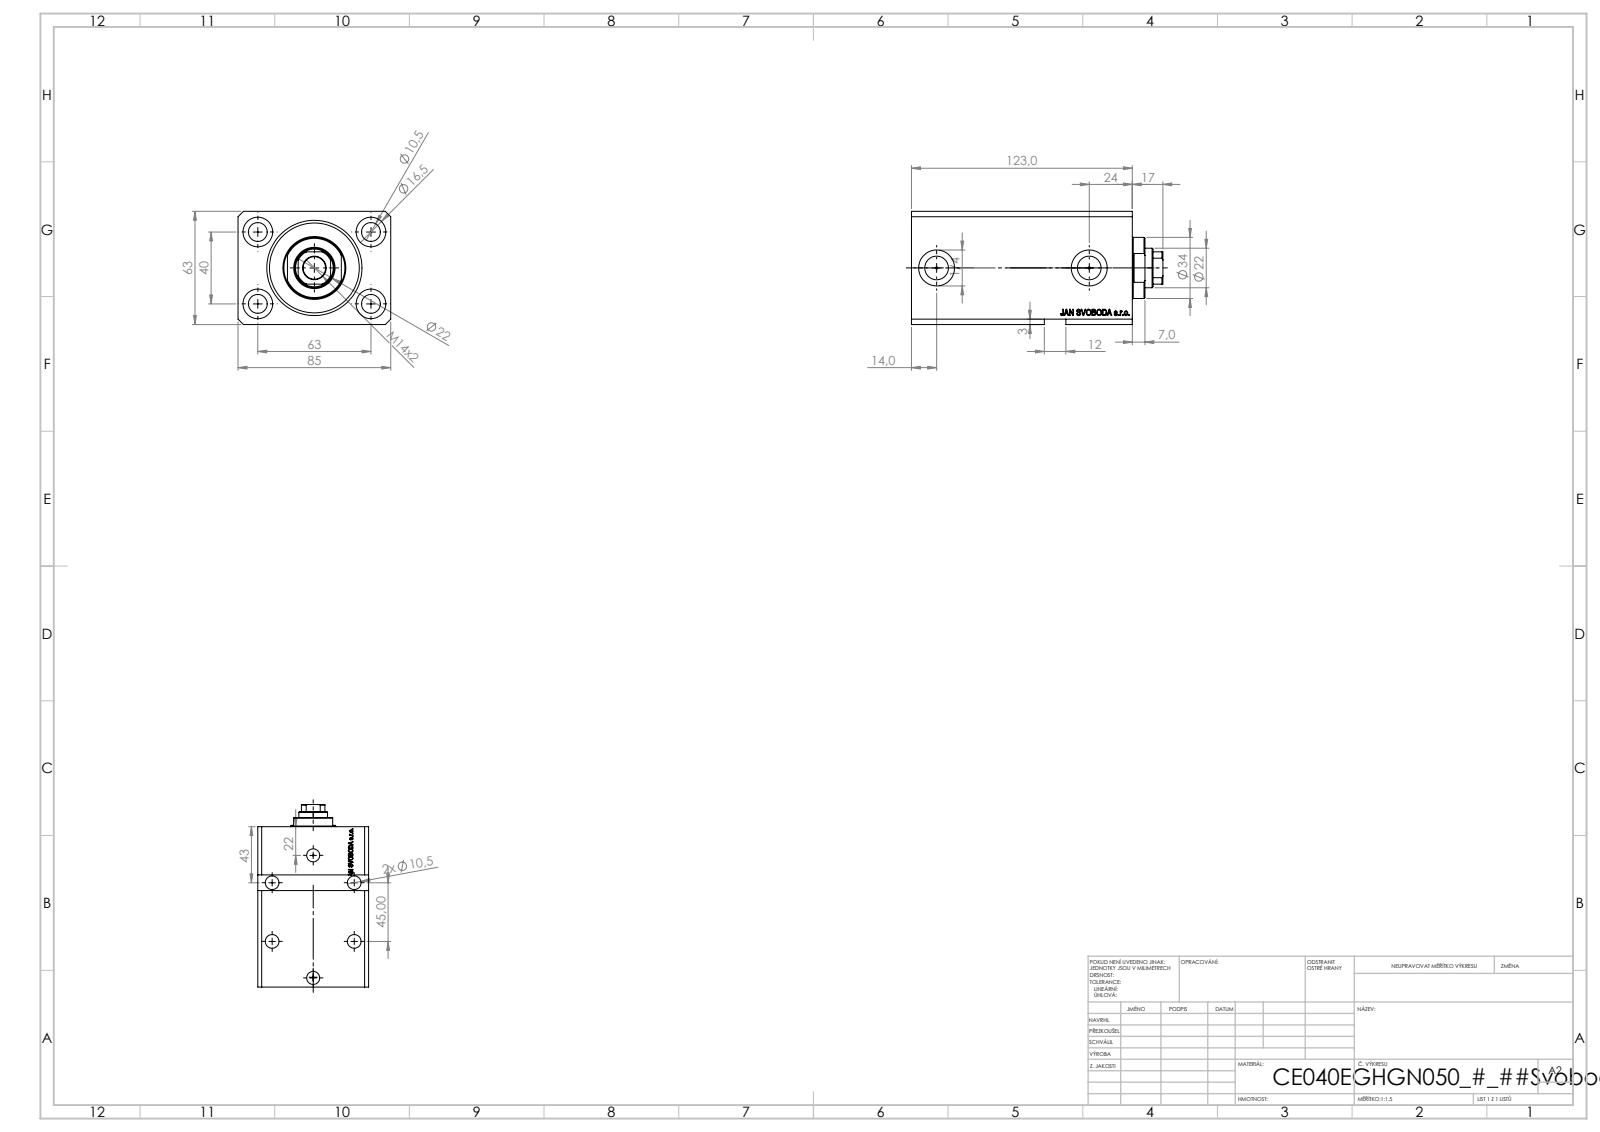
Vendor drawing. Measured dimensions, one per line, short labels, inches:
name: V250CE_C_VCP; V250CE_E_Body; V250CE_VC_E
written by: SolidWorks 2019 (CONFIG_CONTROL_DESIGN)
unit: in
bodies: 3 solids, 937 faces (459 planar, 104 cylindrical, 374 other)
size: 5.512 × 3.346 × 2.48
volume: 33.12 in³; area: 167 in²
holes: 8× ⌀0.413, 4× ⌀0.049, 4× ⌀0.65, 2× ⌀0.394, 2× ⌀0.518, 2× ⌀0.787, 1× ⌀0.492, 1× ⌀0.866, 1× ⌀1.575, 1× ⌀2.087
bosses: 1× ⌀1.339
rounds: 1× R0.413
face distances: 2.48, 3.346, 4.843, 0.669, 4.173, 0.449, 3.724, 4.394, 2.205, 0.433
hole spacings: 1.469, 2.48, 1.491, 1.575, 1.646, 1.659, 1.772, 2.879
